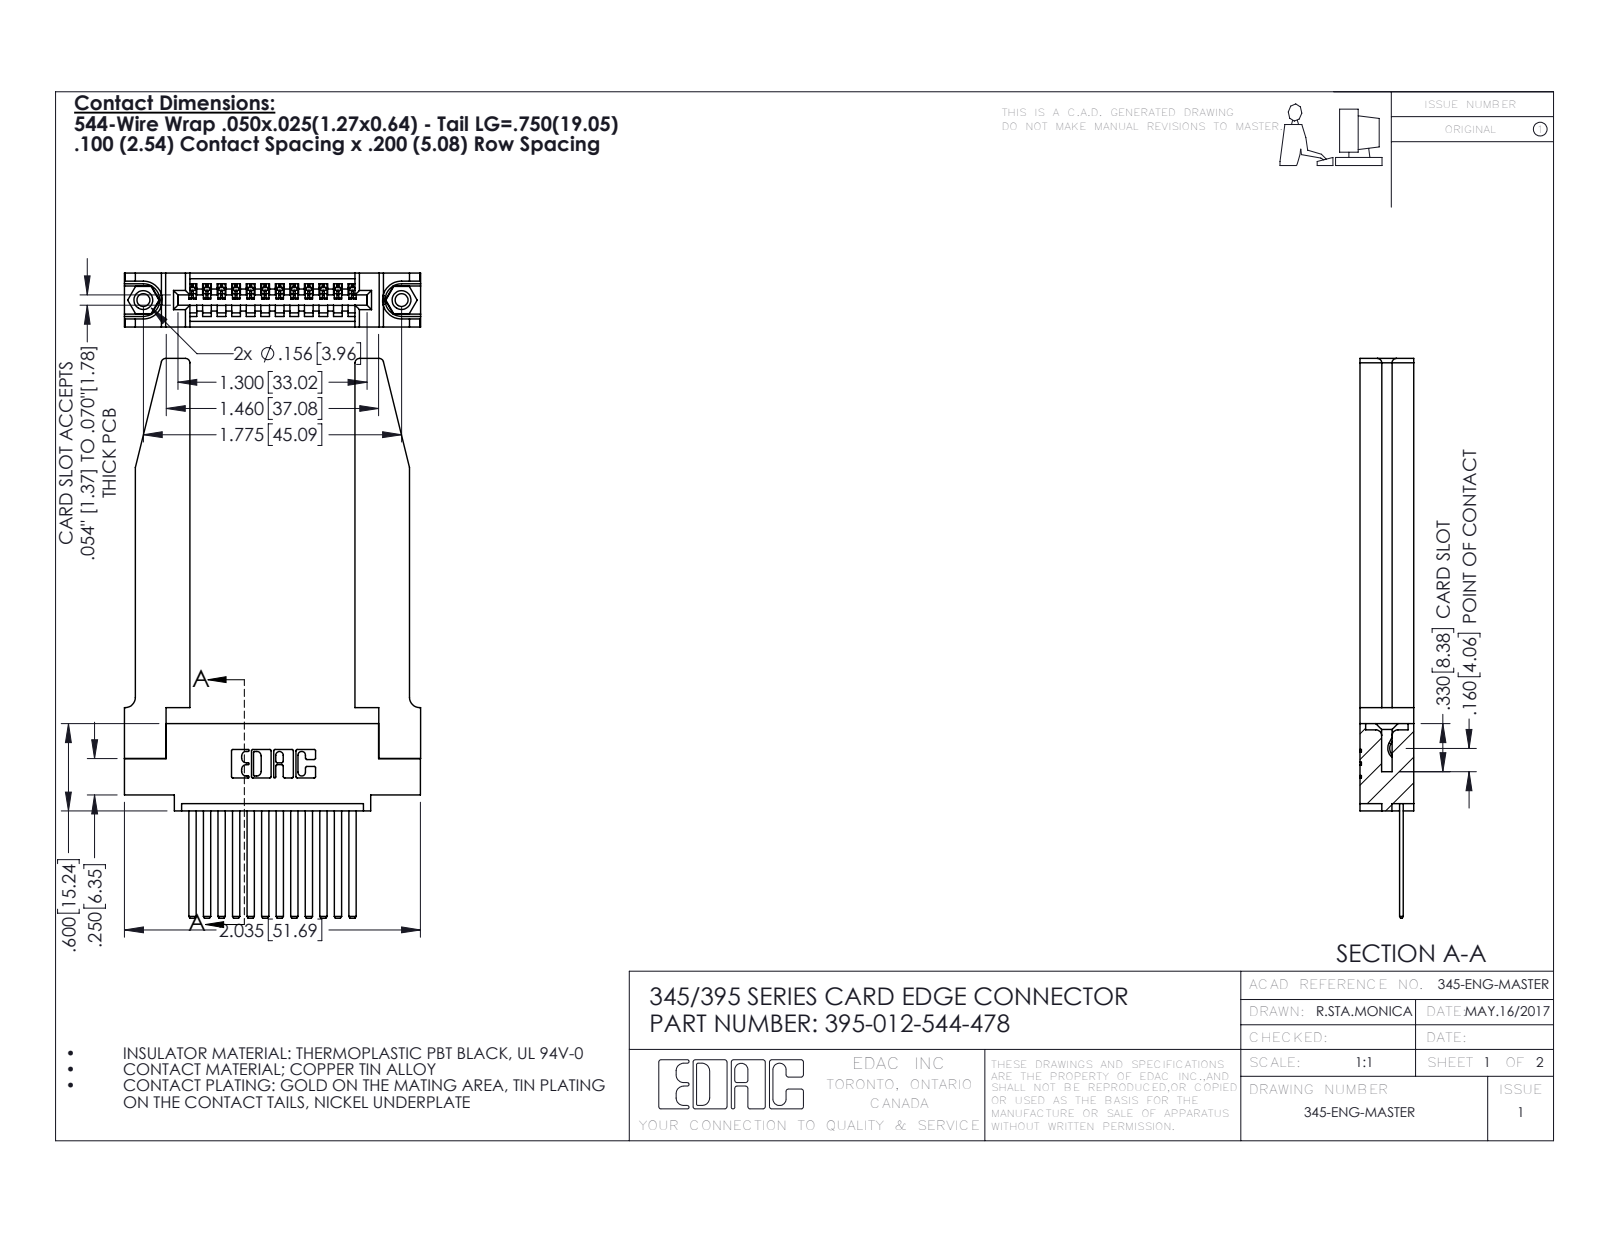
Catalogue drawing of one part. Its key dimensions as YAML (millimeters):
part_name: "345 Part_0.110 Offset - 0.156 Dia-TH; 395-012-544-478; 345-292-001_345-293-144; 345-250-001_345-250-001-102 (+1 more)"
step_written_by: "SolidWorks 2016 (CONFIG_CONTROL_DESIGN)"
units: millimeters
bodies: {solids: 17, faces: 988, planar: 658, cylindrical: 278, other: 52}
overall_size: [97.7, 51.7, 9.4]
volume: 12500
surface_area: 13230
round_holes:
  - {diameter: 2.3, count: 2}
  - {diameter: 3.2, count: 2}
  - {diameter: 4, count: 2}
  - {diameter: 1.6, count: 1}
round_bosses_or_shafts:
  - {diameter: 3.9, count: 2}
partial_cylinders:
  - {radius: 0.2, count: 24}
  - {radius: 0.3, count: 22}
  - {radius: 0.8, count: 8}
  - {radius: 0.2, count: 6}
  - {radius: 0.8, count: 6}
  - {radius: 0.7, count: 3}
  - {radius: 0.8, count: 2}
  - {radius: 1, count: 2}
face_to_face_distances: [9.4, 1.8, 7.6, 2.5, 6.9, 0.6, 3.8, 3.8, 5.6, 2]
hole_center_spacings: [6.9, 39.2, 45.1]
